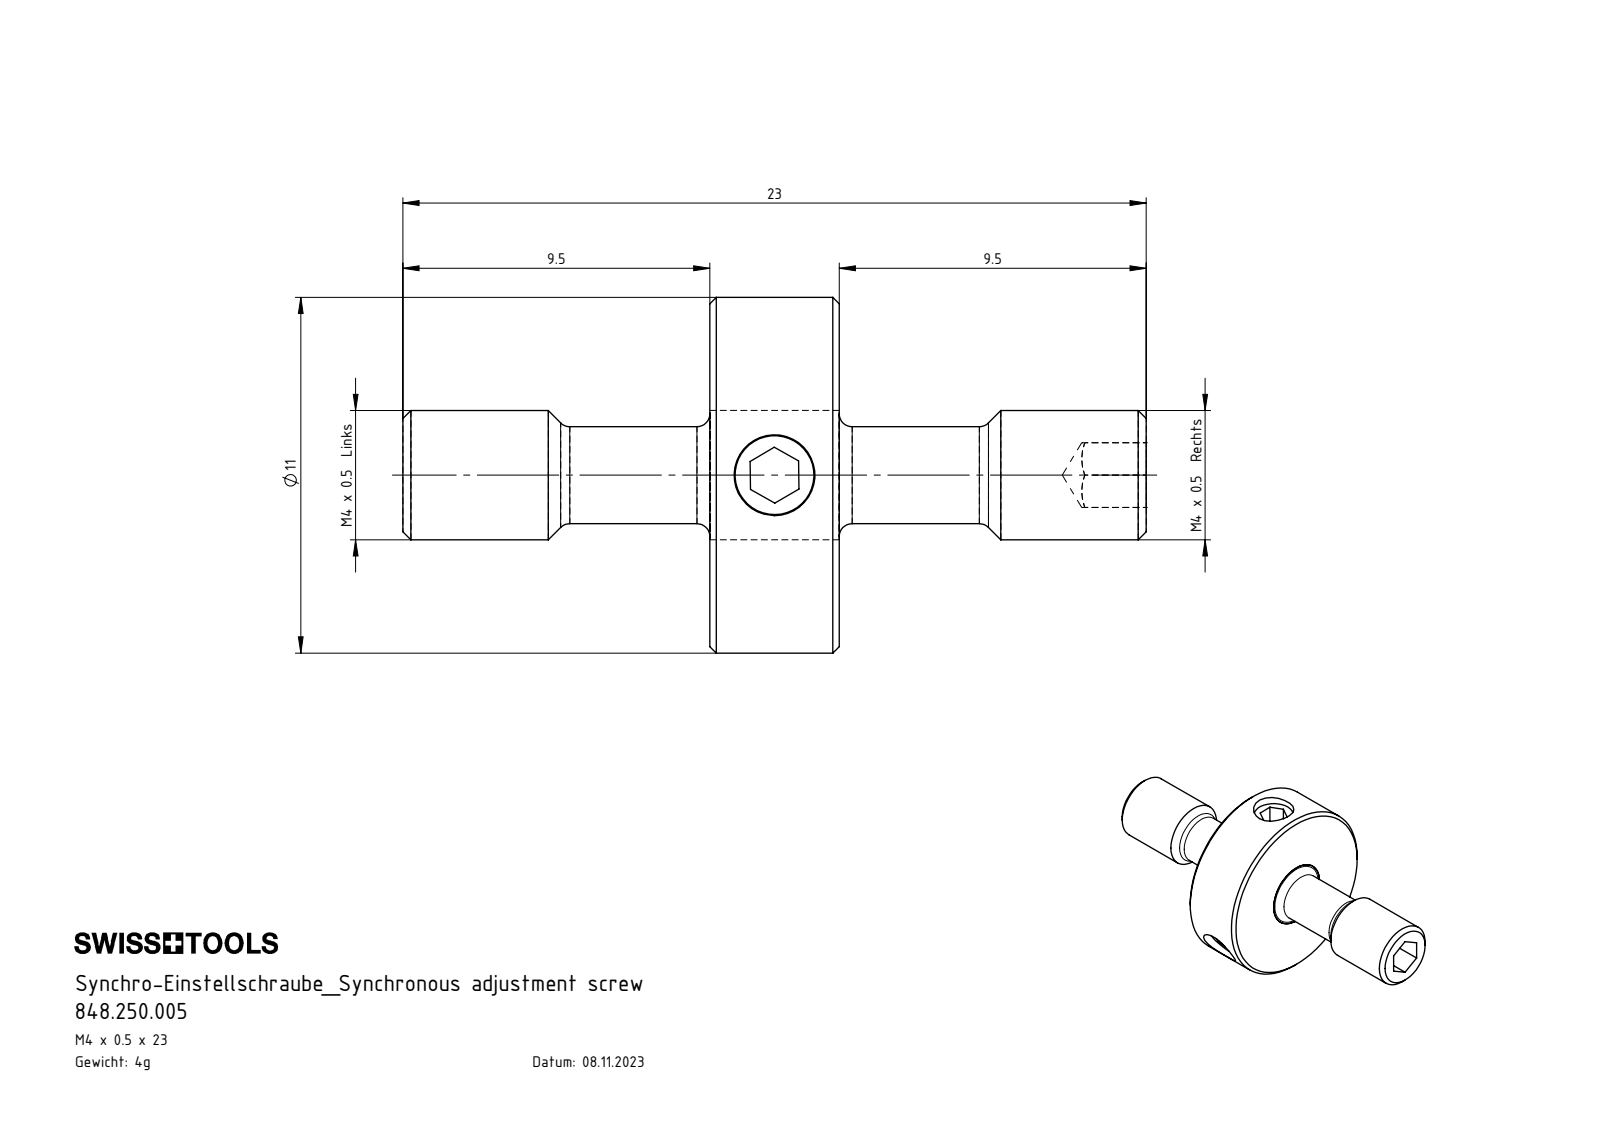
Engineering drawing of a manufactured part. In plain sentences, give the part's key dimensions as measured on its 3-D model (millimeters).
The part is named "Z25-ER3.001.023_A; ISO 4026 - M3 x 3; 848.250.005; Z25-ER3.002.004_A". Its 3-D file was written by "SolidWorks 2022 (AUTOMOTIVE_DESIGN)". It is 5 solids with 99 faces: 39 planar, 26 cylindrical and 34 other. Overall it measures 23 by 11 by 11 millimeters. Its volume is 553 cubic millimeters and its surface area 853 square millimeters. Round holes: 3 of diameter 2.5. Round bosses or shafts: 4 of diameter 3, 1 of diameter 11, 1 of diameter 4. The main face-to-face distances are 4, 9.5, 13.5, 1.5, 2, 3, 10.75, 12.25, 1.25, 2.75.
